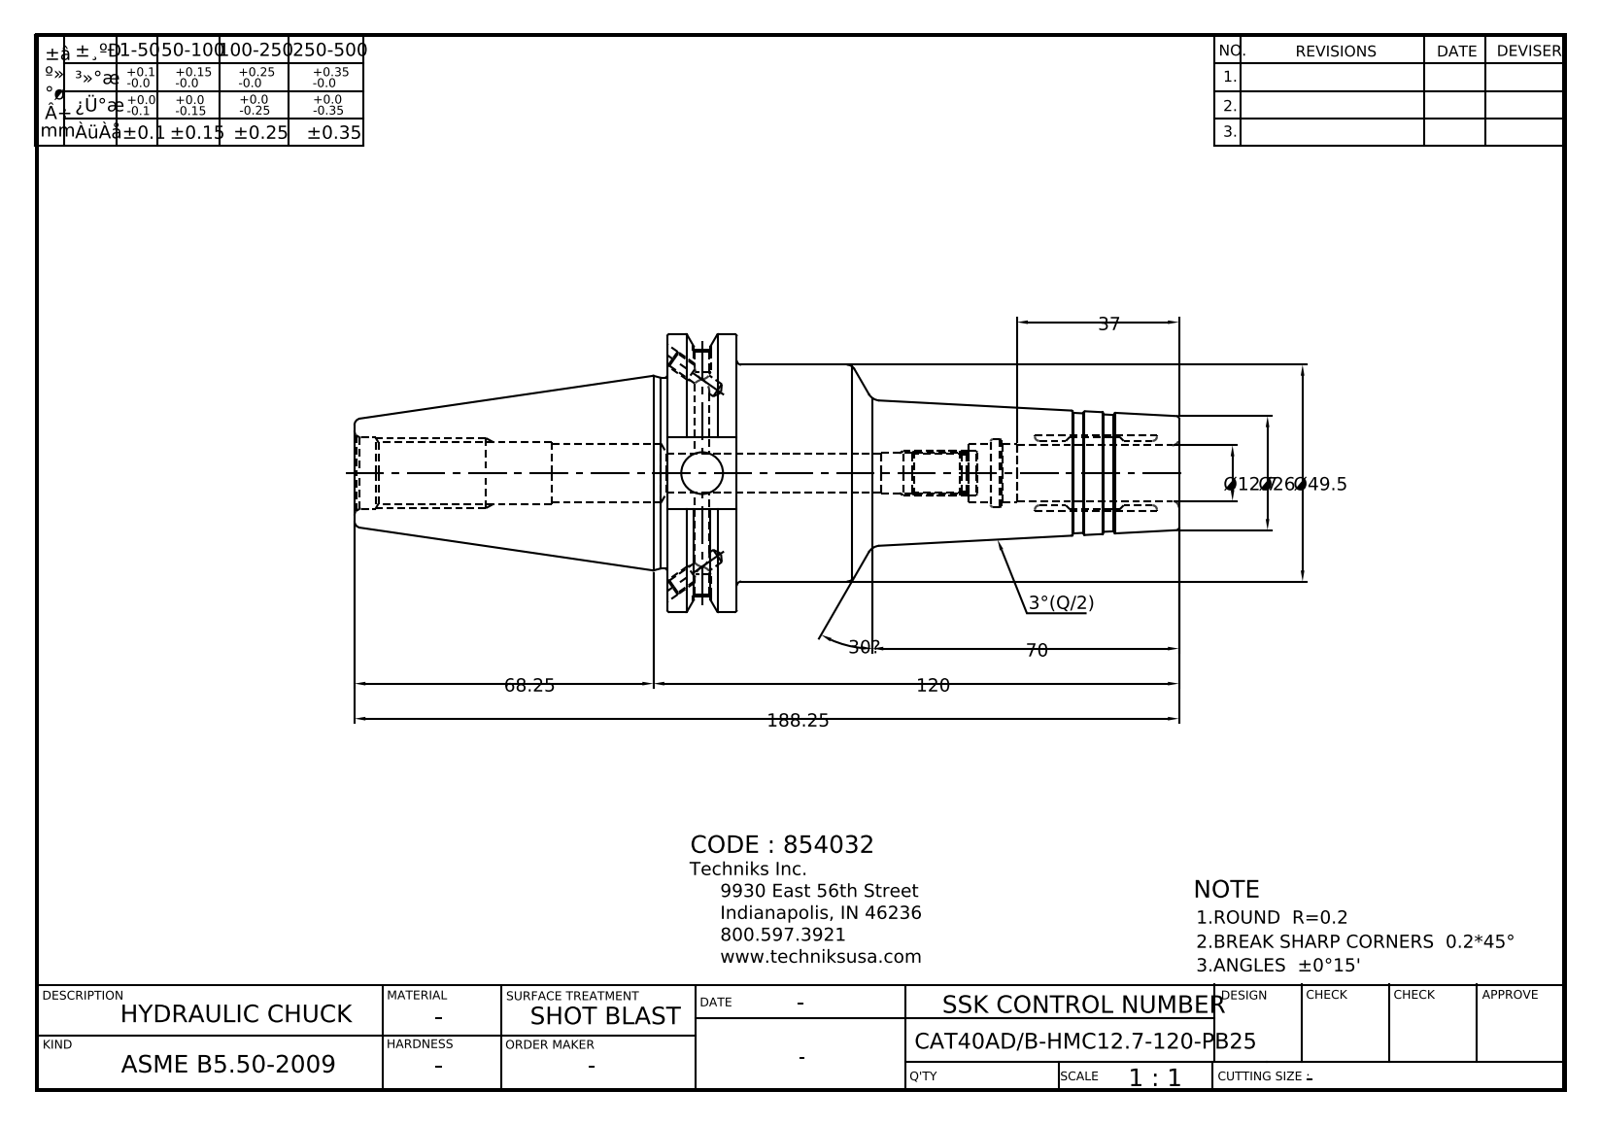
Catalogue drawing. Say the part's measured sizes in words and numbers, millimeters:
The part is named "CAT40ADB-HMC1_2-4_72-854032". Its 3-D file was written by "PRO/ENGINEER BY PARAMETRIC TECHNOLOGY CORPORATION, 2015200 (CONFIG_CONTROL_DESIGN)". It is 1 solid with 159 faces: 57 planar, 56 cylindrical and 46 other. Overall it measures 188.25 by 63.5 by 60.84 millimeters. Its volume is 201 381 cubic millimeters and its surface area 34 856 square millimeters. Round holes: 3 of diameter 3.3, 3 of diameter 4, 1 of diameter 4.2, 1 of diameter 9.53, 1 of diameter 11.1, 1 of diameter 12.7, 1 of diameter 13.49, 1 of diameter 15.88, 1 of diameter 16.3. Round bosses or shafts: 1 of diameter 63.5, 1 of diameter 49.5, 1 of diameter 43.6. Partial cylindrical surfaces (rounded edges, fillets, slot ends): 1 of radius 28.15. The main face-to-face distances are 15.88, 116.83, 100.95, 47.6, 71.42, 87.3, 188.25, 16.38, 151.25, 79.83.
